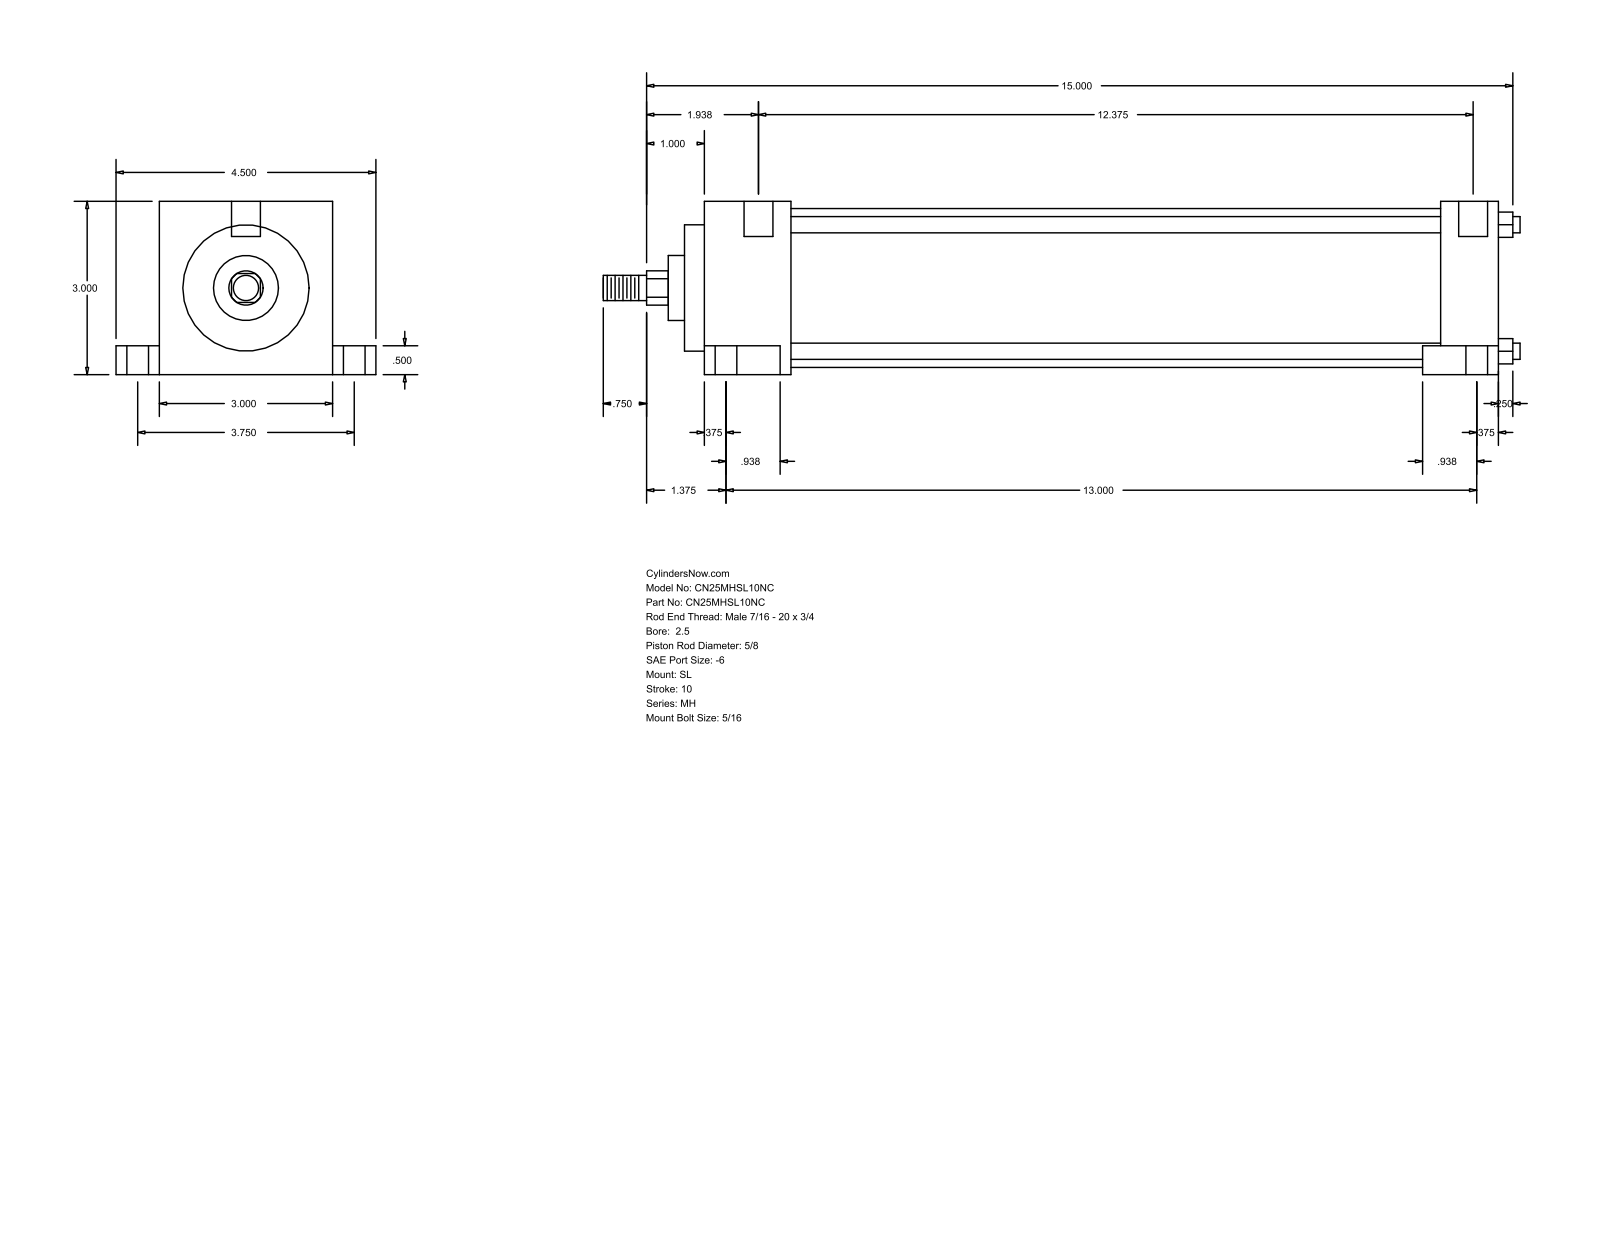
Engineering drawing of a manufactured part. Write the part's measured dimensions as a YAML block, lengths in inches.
part_name: "MH_SL__0250_0.625"
step_written_by: "GSSL Pune (CONFIG_CONTROL_DESIGN)"
units: inches
bodies: {solids: 0, faces: 86, planar: 61, cylindrical: 25, other: 0}
overall_size: [15.875, 4.5, 3]
round_holes:
  - {diameter: 0.219, count: 2}
  - {diameter: 0.375, count: 2}
  - {diameter: 0.625, count: 2}
  - {diameter: 0.5, count: 1}
round_bosses_or_shafts:
  - {diameter: 0.281, count: 4}
  - {diameter: 2.75, count: 1}
  - {diameter: 2.187, count: 1}
  - {diameter: 1.125, count: 1}
  - {diameter: 0.625, count: 1}
  - {diameter: 0.437, count: 1}
partial_cylinders:
  - {radius: 0.297, count: 1}
face_to_face_distances: [3, 1, 13.094, 14.094, 2.5, 0.5, 0.75, 3.75, 1.25, 12.781]
hole_center_spacings: [1.876, 0.125, 3.75]
